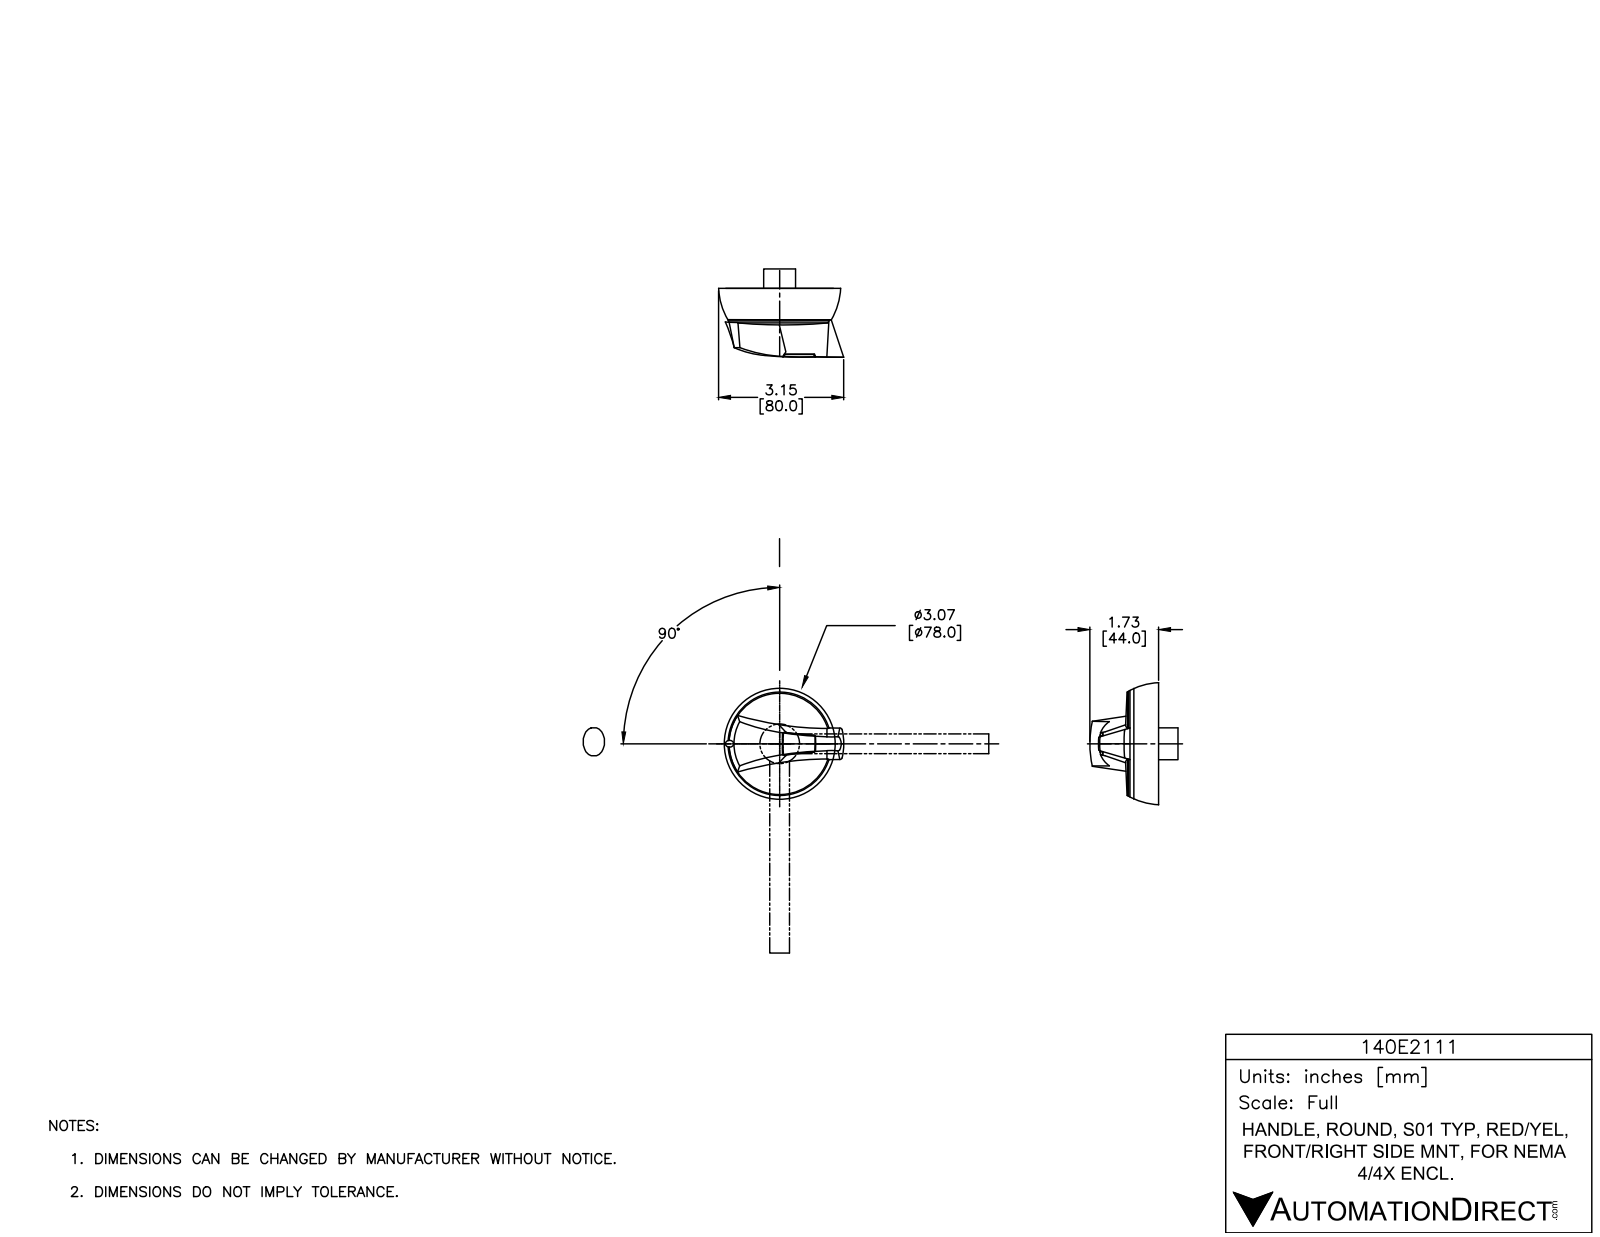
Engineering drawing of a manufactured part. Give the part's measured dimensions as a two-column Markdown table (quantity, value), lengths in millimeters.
| quantity | value |
| --- | --- |
| part name | 140E2111 |
| STEP written by | SolidWorks 2015 (AUTOMOTIVE_DESIGN) |
| units | millimeters |
| bodies | 9 solids, 1345 faces (711 planar, 526 cylindrical, 108 other) |
| overall size | 79.9 × 78 × 51.5 |
| volume | 132 400 mm³ |
| surface area | 36 780 mm² |
| round holes (diameter × count) | 4 × 6, 10.8 × 4, 0.8 × 3, 4.3 × 2, 8.6 × 2, 9.2 × 2, 4.8 × 1, 76 × 1 |
| round bosses / shafts (diameter × count) | 0.5 × 11, 8 × 4, 2.3 × 3, 1.8 × 3, 5.8 × 2, 71.6 × 1, 68.6 × 1, 66.8 × 1 |
| partial cylindrical surfaces (radius × count) | 0.3 × 221, 0.4 × 20, 0.9 × 20, 0.8 × 15, 0.6 × 3, 200 × 2, 0.3 × 1, 2 × 1 |
| main face-to-face distances | 0.6, 15.8, 39.1, 23.3, 0.9, 15.5, 38.8, 15.2, 38.5, 6.2 |
| hole center spacings | 24.4, 7.8, 27.9, 28, 30.6, 40, 47.8, 48.8 |
